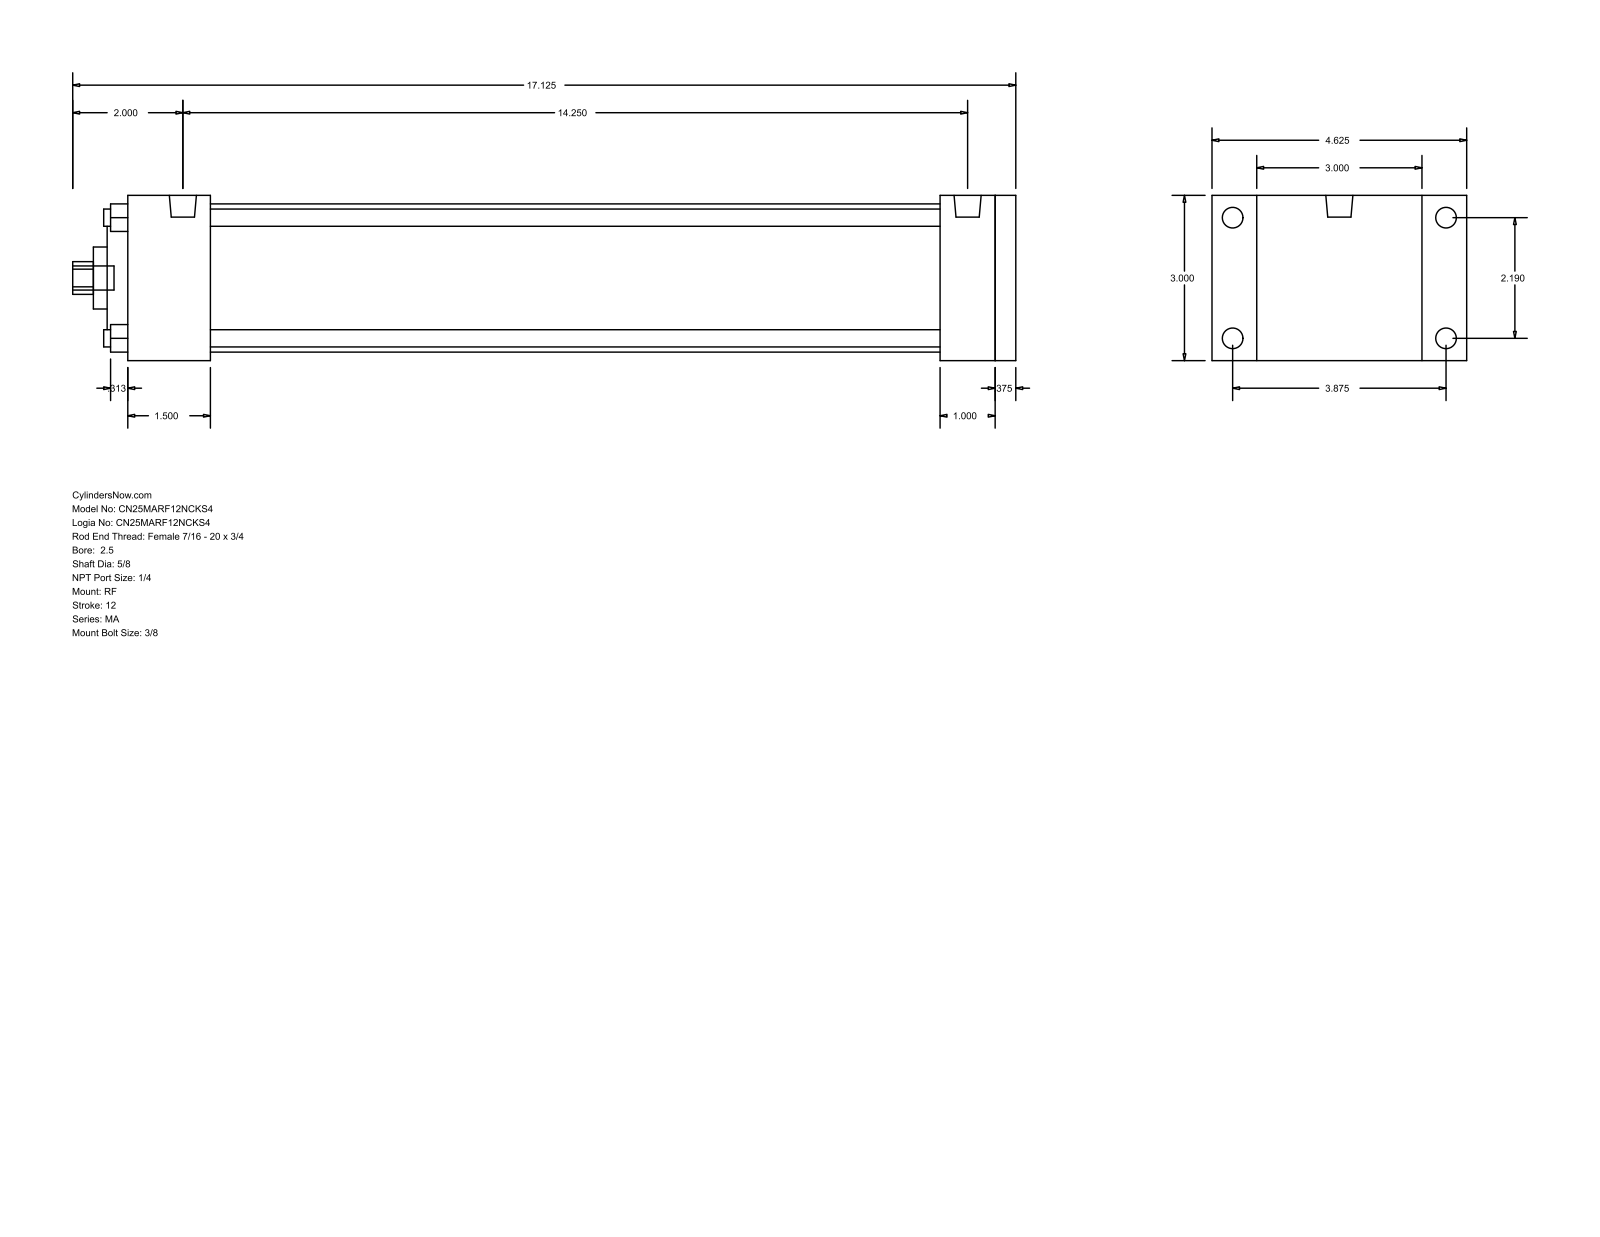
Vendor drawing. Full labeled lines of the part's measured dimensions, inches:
Part name (STEP PRODUCT): MA_RF__0250_0.625
STEP written by: GSSL Pune (CONFIG_CONTROL_DESIGN)
Units: inches
Bodies: 0 solids, 94 faces (65 planar, 29 cylindrical, 0 other)
Overall size (bounding box): 17.125 × 4.625 × 3
Round holes (diameter × count): ⌀0.313 ×4, ⌀0.625 ×1, ⌀1.125 ×1, ⌀2 ×1, ⌀2.69 ×1
Round bosses / shafts (diameter × count): ⌀0.375 ×4, ⌀0.313 ×4, ⌀0.492 ×2, ⌀0.437 ×1
Partial cylindrical surfaces — rounded edges, fillets, slot ends (radius × count): R0.297 ×1
Main face-to-face distances: 3, 16.125, 0.375, 15.75, 1, 1.5, 14.75, 13.25, 14.25, 14.625
Hole centre spacings: 1.548, 2.19, 3.097
